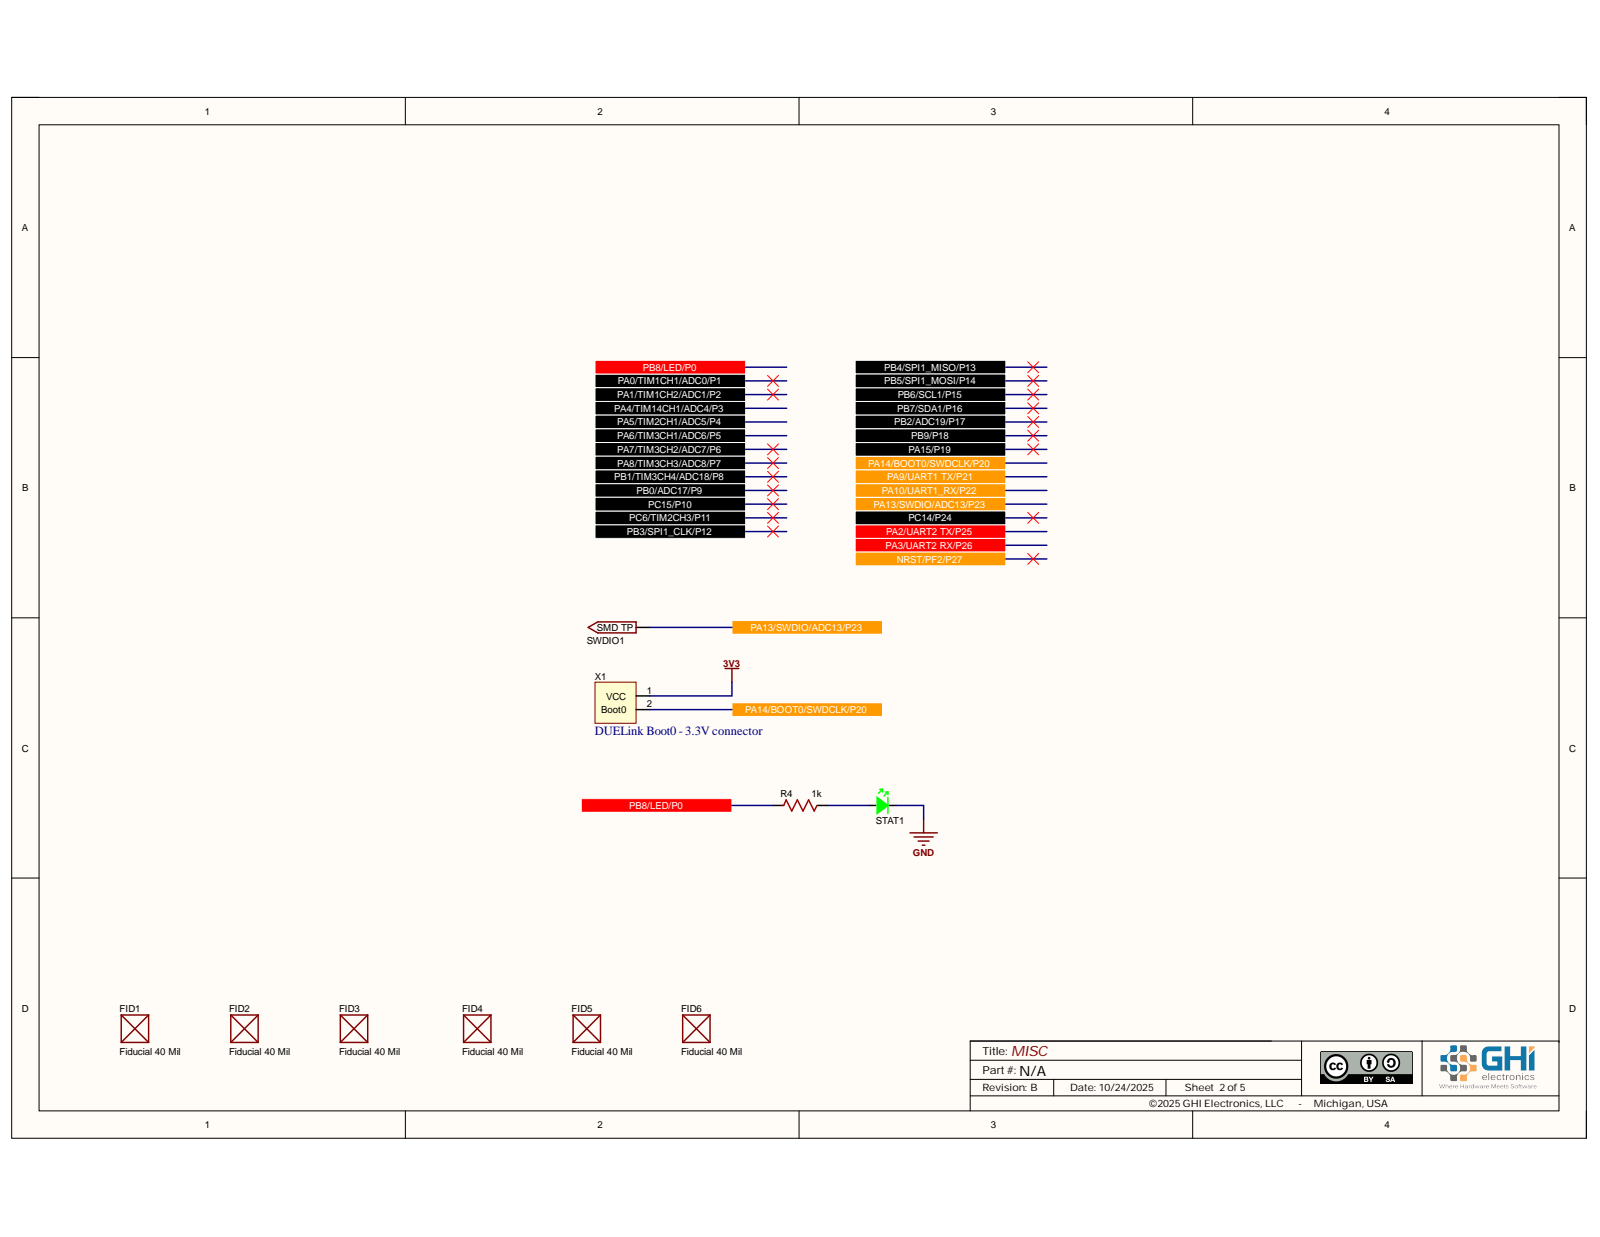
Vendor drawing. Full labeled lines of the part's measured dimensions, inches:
Part name (STEP PRODUCT): PCB; Board; STAT1; 0603 LED Green (+5 more)
STEP written by: Open CASCADE 7.5 (AUTOMOTIVE_DESIGN)
Units: inches
Bodies: 100 solids, 1487 faces (1115 planar, 260 cylindrical, 112 other)
Overall size (bounding box): 1.427 × 1.26 × 1.26
Volume: 0.491 in³ · Surface area: 12.75 in²
Round holes (diameter × count): ⌀0.035 ×6, ⌀0.035 ×4, ⌀0.055 ×4, ⌀0.118 ×4, ⌀0.04 ×2, ⌀0.19 ×2, ⌀0.24 ×2
Round bosses / shafts (diameter × count): ⌀0.145 ×2, ⌀0.44 ×1, ⌀0.25 ×1, ⌀0.12 ×1, ⌀0.11 ×1
Partial cylindrical surfaces — rounded edges, fillets, slot ends (radius × count): R0.005 ×35, R0.006 ×14, R0.138 ×4, R0.007 ×2, R0.007 ×2, R0.007 ×2, R0.02 ×2, R0.18 ×2
Main face-to-face distances: 0.063, 0.533, 0.47, 0.02, 0.625, 0.625, 0.73, 0.75, 0.12, 0.505
Hole centre spacings: 0.1, 0.2, 0.984, 0.797, 0.125, 0.14, 0.179, 0.191
